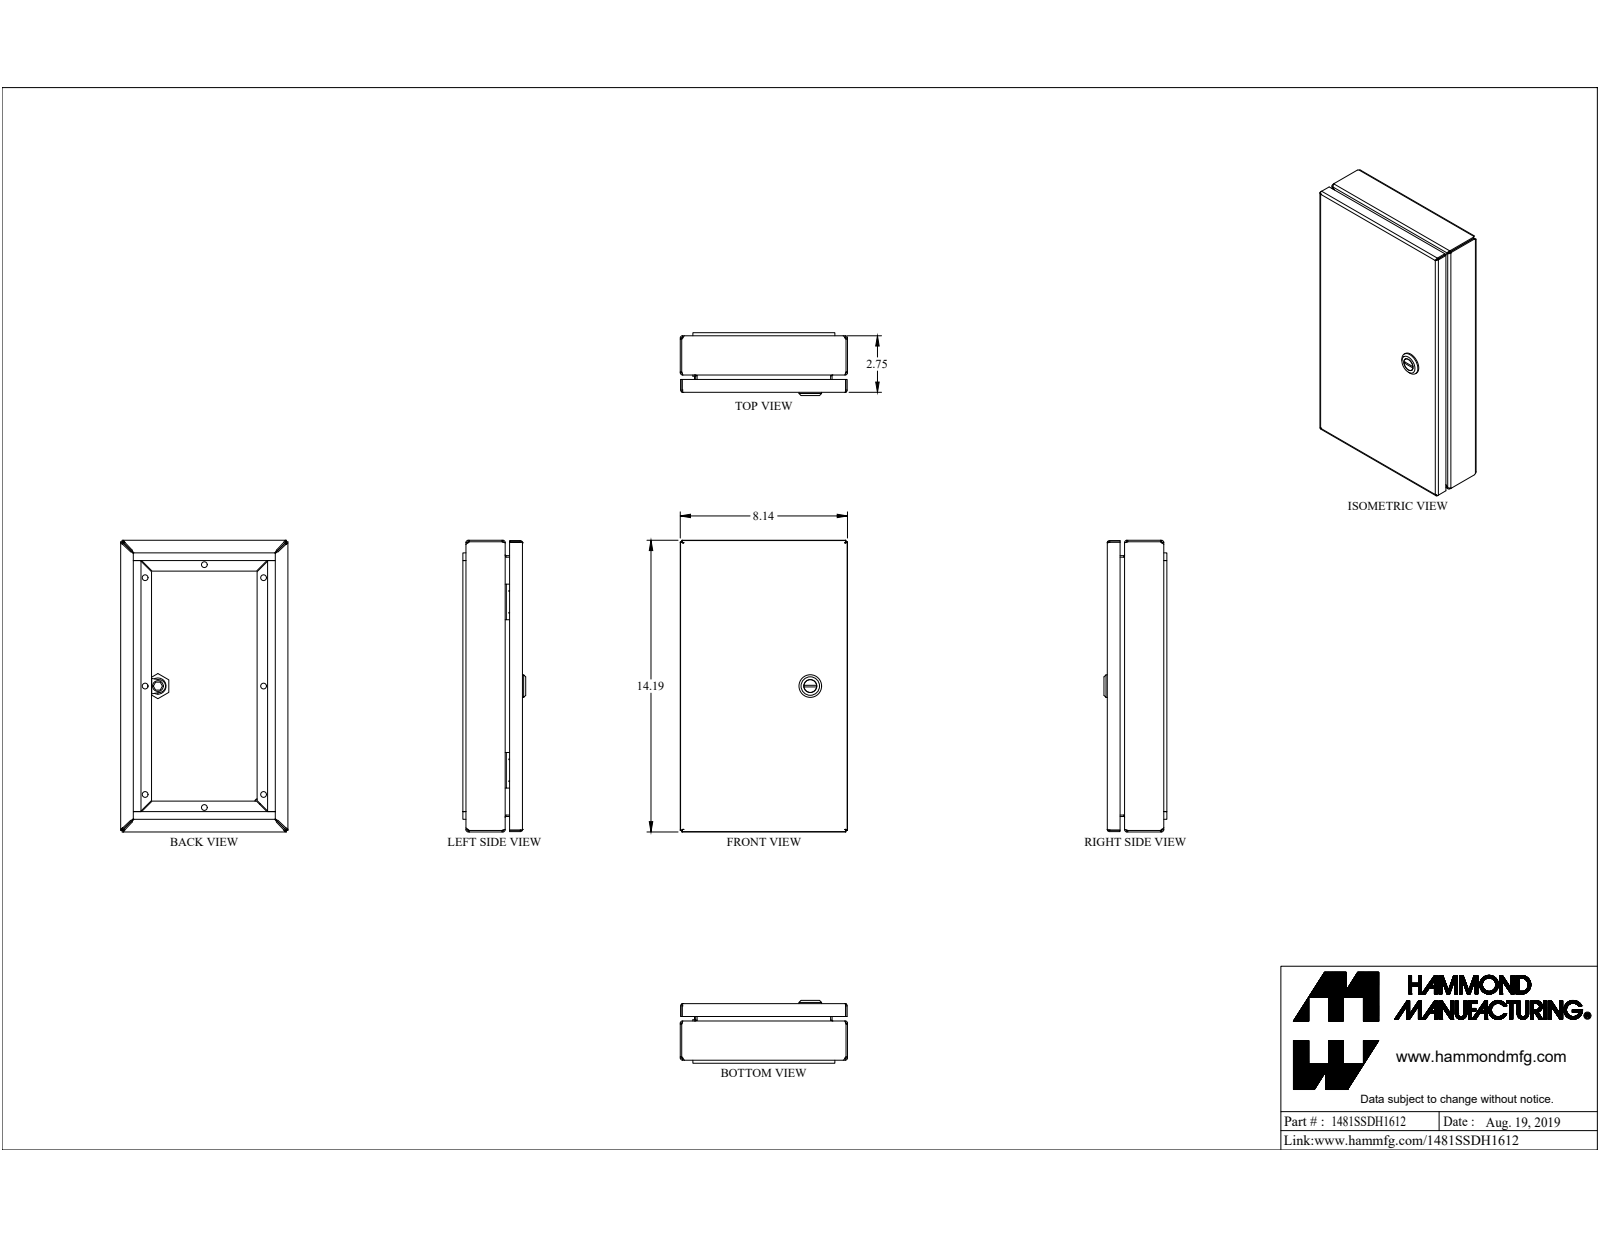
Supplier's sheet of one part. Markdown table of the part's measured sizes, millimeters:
| quantity | value |
| --- | --- |
| part name | 1481SSDH1612 |
| STEP written by | SolidWorks 2019 (CONFIG_CONTROL_DESIGN) |
| units | millimeters |
| bodies | 24 solids, 618 faces (374 planar, 147 cylindrical, 97 other) |
| overall size | 360.4 × 206.8 × 77.7 |
| volume | 531 600 mm³ |
| surface area | 542 500 mm² |
| round holes (diameter × count) | 7.1 × 8, 4.4 × 1, 5 × 1, 6.1 × 1, 6.1 × 1, 9.8 × 1, 12.7 × 1, 16 × 1, 19.5 × 1 |
| round bosses / shafts (diameter × count) | 27.9 × 1, 19.9 × 1, 15.9 × 1, 13.3 × 1, 12.1 × 1, 10.1 × 1, 9 × 1, 8 × 1 |
| partial cylindrical surfaces (radius × count) | 0.9 × 28, 2.7 × 28, 0.2 × 4, 1.6 × 4, 6.4 × 4, 12.7 × 4, 3.2 × 2, 0.5 × 1 |
| main face-to-face distances | 1.8, 65.5, 21.4, 44.1, 204.9, 67.3, 68, 46.6, 2.5, 63.7 |
| hole center spacings | 75, 293.2, 146.4, 133.9, 133.9, 166.9, 166.9, 198.4 |
